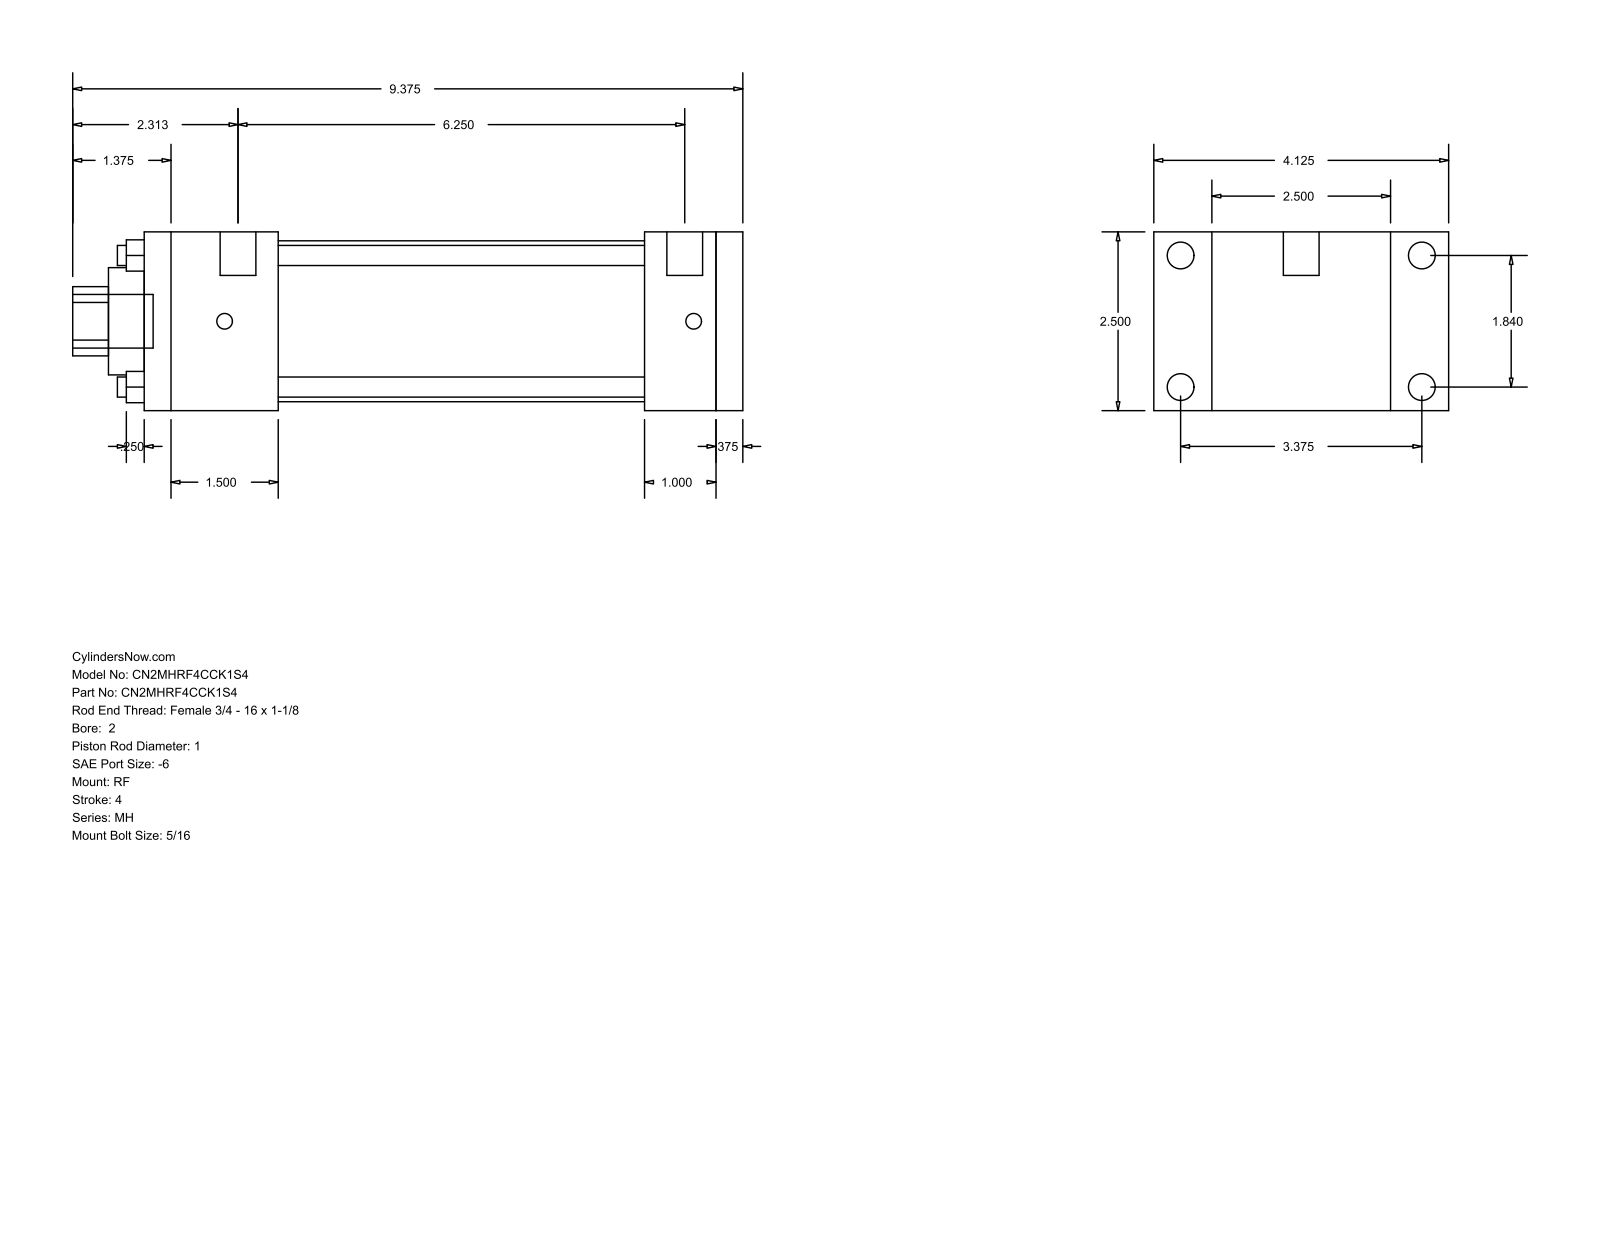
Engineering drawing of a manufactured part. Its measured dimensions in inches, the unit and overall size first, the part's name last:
Units: inches
Overall size (bounding box): 9.375 × 4.125 × 2.5
Round holes (diameter × count): ⌀0.281 ×4, ⌀1 ×1, ⌀1.5 ×1, ⌀2.25 ×1
Round bosses / shafts (diameter × count): ⌀0.375 ×4, ⌀0.219 ×4, ⌀0.5 ×2, ⌀0.75 ×1
Partial cylindrical surfaces — rounded edges, fillets, slot ends (radius × count): R0.484 ×1
Main face-to-face distances: 2.5, 0.375, 8.375, 8, 0.813, 1, 1.875, 7, 5.125, 6.125
Hole centre spacings: 1.301, 1.84, 2.602
Bodies: 0 solids, 92 faces (64 planar, 28 cylindrical, 0 other)
Part name (STEP PRODUCT): MH_RF__0200_1
STEP written by: GSSL Pune (CONFIG_CONTROL_DESIGN)
